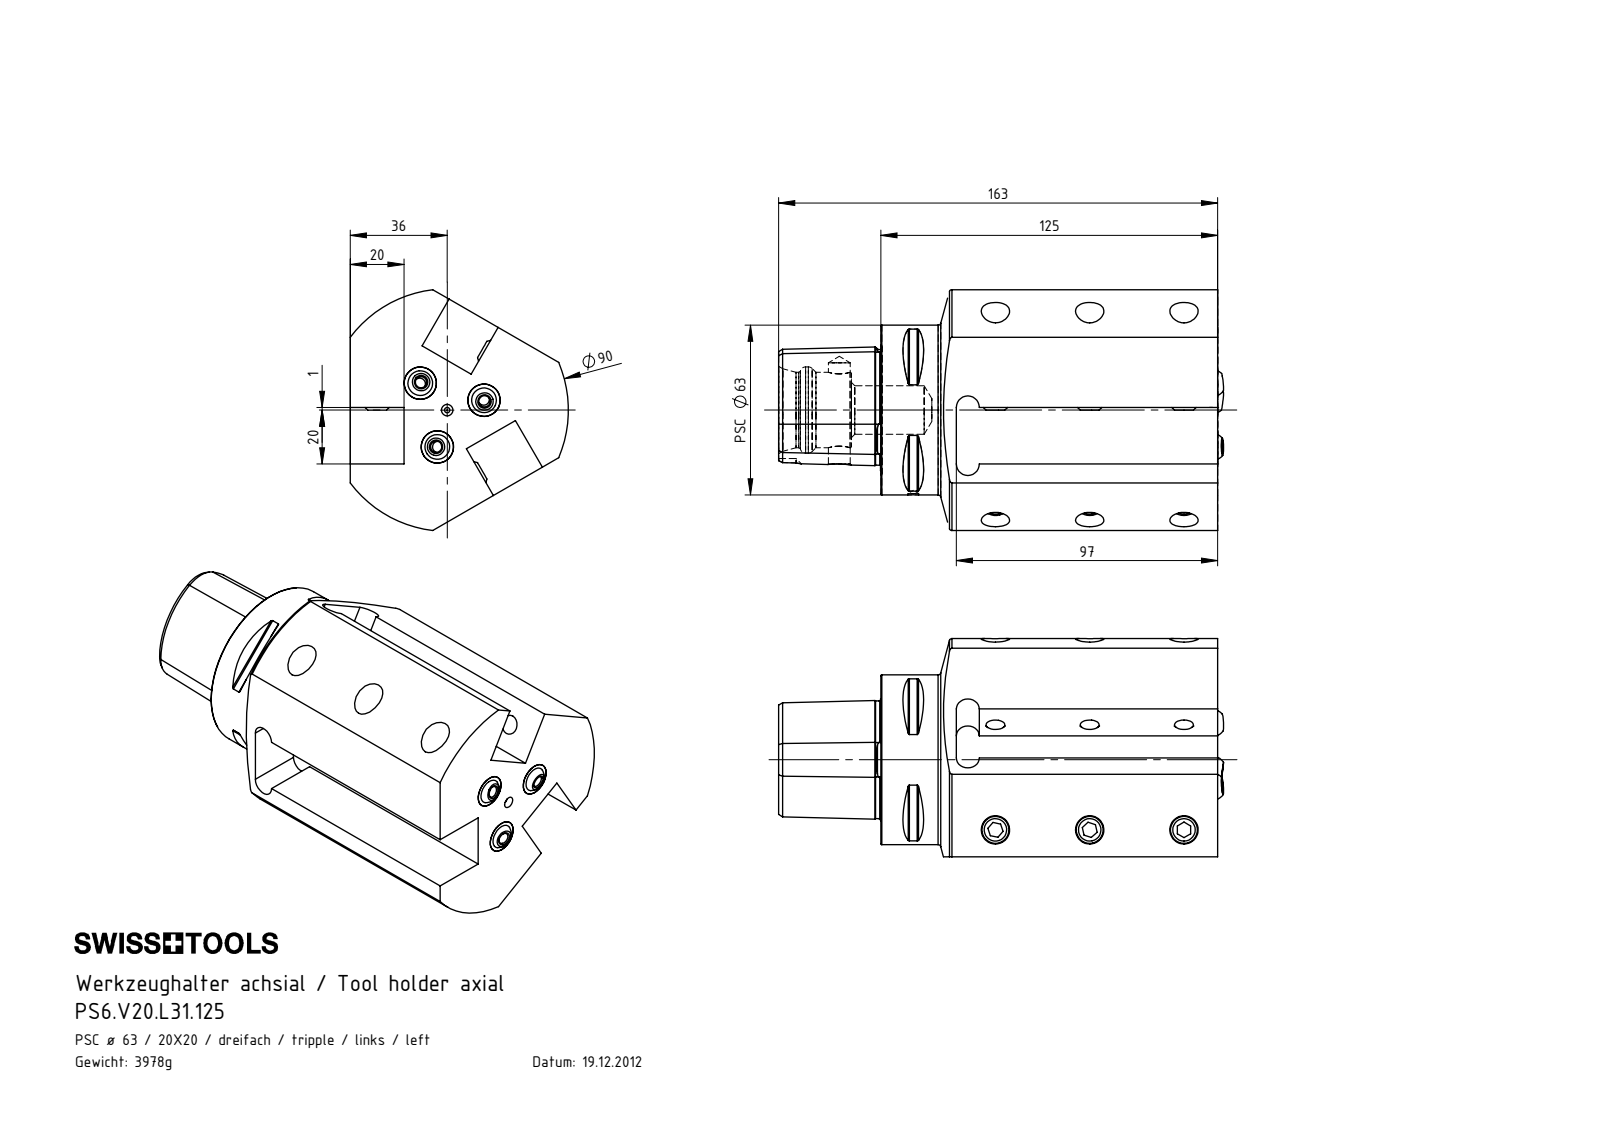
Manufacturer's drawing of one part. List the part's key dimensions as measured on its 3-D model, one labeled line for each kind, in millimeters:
Part name (STEP PRODUCT): ISO 4026 - M10 x 25; KU1-U12.001.010; PS6-V20.L31.125; KU1-U12.001.010_1 (+2 more)
STEP written by: SolidWorks 2012 (CONFIG_CONTROL_DESIGN)
Units: millimetres
Bodies: 16 solids, 419 faces (127 planar, 124 cylindrical, 168 other)
Overall size (bounding box): 165.19 × 89.35 × 81
Volume: 499 602 mm³ · Surface area: 89 333 mm²
Round holes (diameter × count): ⌀8.5 ×10, ⌀12.5 ×9, ⌀4.2 ×3, ⌀5 ×3, ⌀7 ×3, ⌀12 ×3, ⌀2 ×1, ⌀4 ×1, ⌀8.1 ×1, ⌀18 ×1, ⌀28 ×1, ⌀32 ×1
Round bosses / shafts (diameter × count): ⌀10 ×9, ⌀63 ×1
Partial cylindrical surfaces — rounded edges, fillets, slot ends (radius × count): R0.5 ×8, R5.1 ×6, R6 ×1, R45 ×1
Main face-to-face distances: 20, 21, 97, 28, 125, 117, 89, 8, 5, 38
Hole centre spacings: 35, 14.14, 24.49, 70, 27.5, 40.08, 63.56, 70.47
